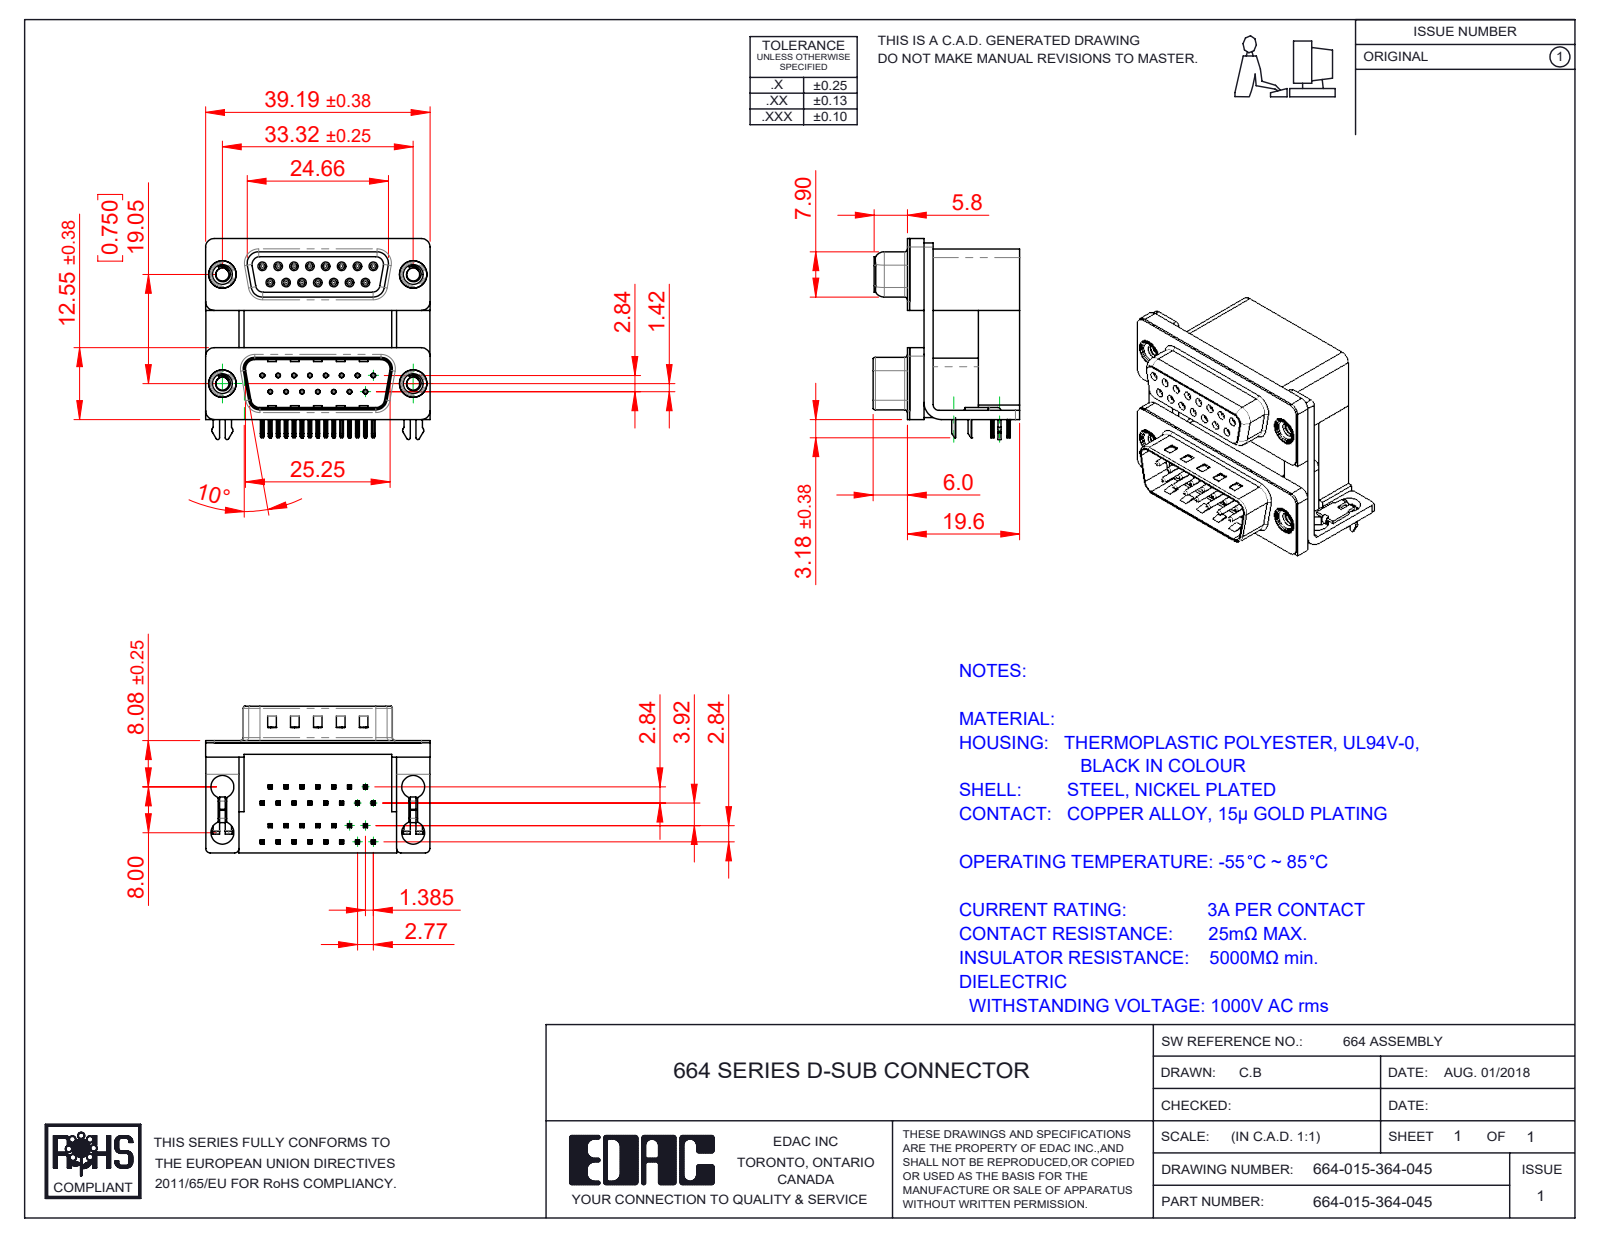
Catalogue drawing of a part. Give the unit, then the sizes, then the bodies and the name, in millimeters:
Units: millimetres
Overall size (bounding box): 39.19 × 35.1 × 25.6
Round holes (diameter × count): ⌀0.8 ×30, ⌀0.35 ×15, ⌀0.9 ×15, ⌀4 ×8, ⌀2.26 ×4, ⌀3.5 ×4, ⌀4.8 ×4, ⌀5 ×4
Round bosses / shafts (diameter × count): ⌀1.2 ×15, ⌀0.75 ×15, ⌀4.9 ×4, ⌀4.75 ×4, ⌀3.9 ×4
Partial cylindrical surfaces — rounded edges, fillets, slot ends (radius × count): R0.1 ×121, R0.25 ×66, R0.15 ×60, R0.12 ×30, R0.35 ×30, R0.5 ×16, R1.5 ×16, R0.34 ×15
Main face-to-face distances: 0.4, 19.2, 16.7, 2.5, 7.2, 12, 9.5, 10.69, 2.19, 2.9
Hole centre spacings: 3.16, 2.77, 19.25, 5.54, 19.84, 8.31, 19.05, 20.78
Volume: 15 167 mm³ · Surface area: 17 004 mm²
Bodies: 43 solids, 4020 faces (2093 planar, 1044 cylindrical, 883 other)
Part name (STEP PRODUCT): 664 Shell Receptacle_15 Contacts; 664 Contact Bottom Lower; 664 2 Prong Board Lock_4; 664 Housing Upper_15 Contacts M (+8 more)
STEP written by: SolidWorks 2020 (CONFIG_CONTROL_DESIGN)
